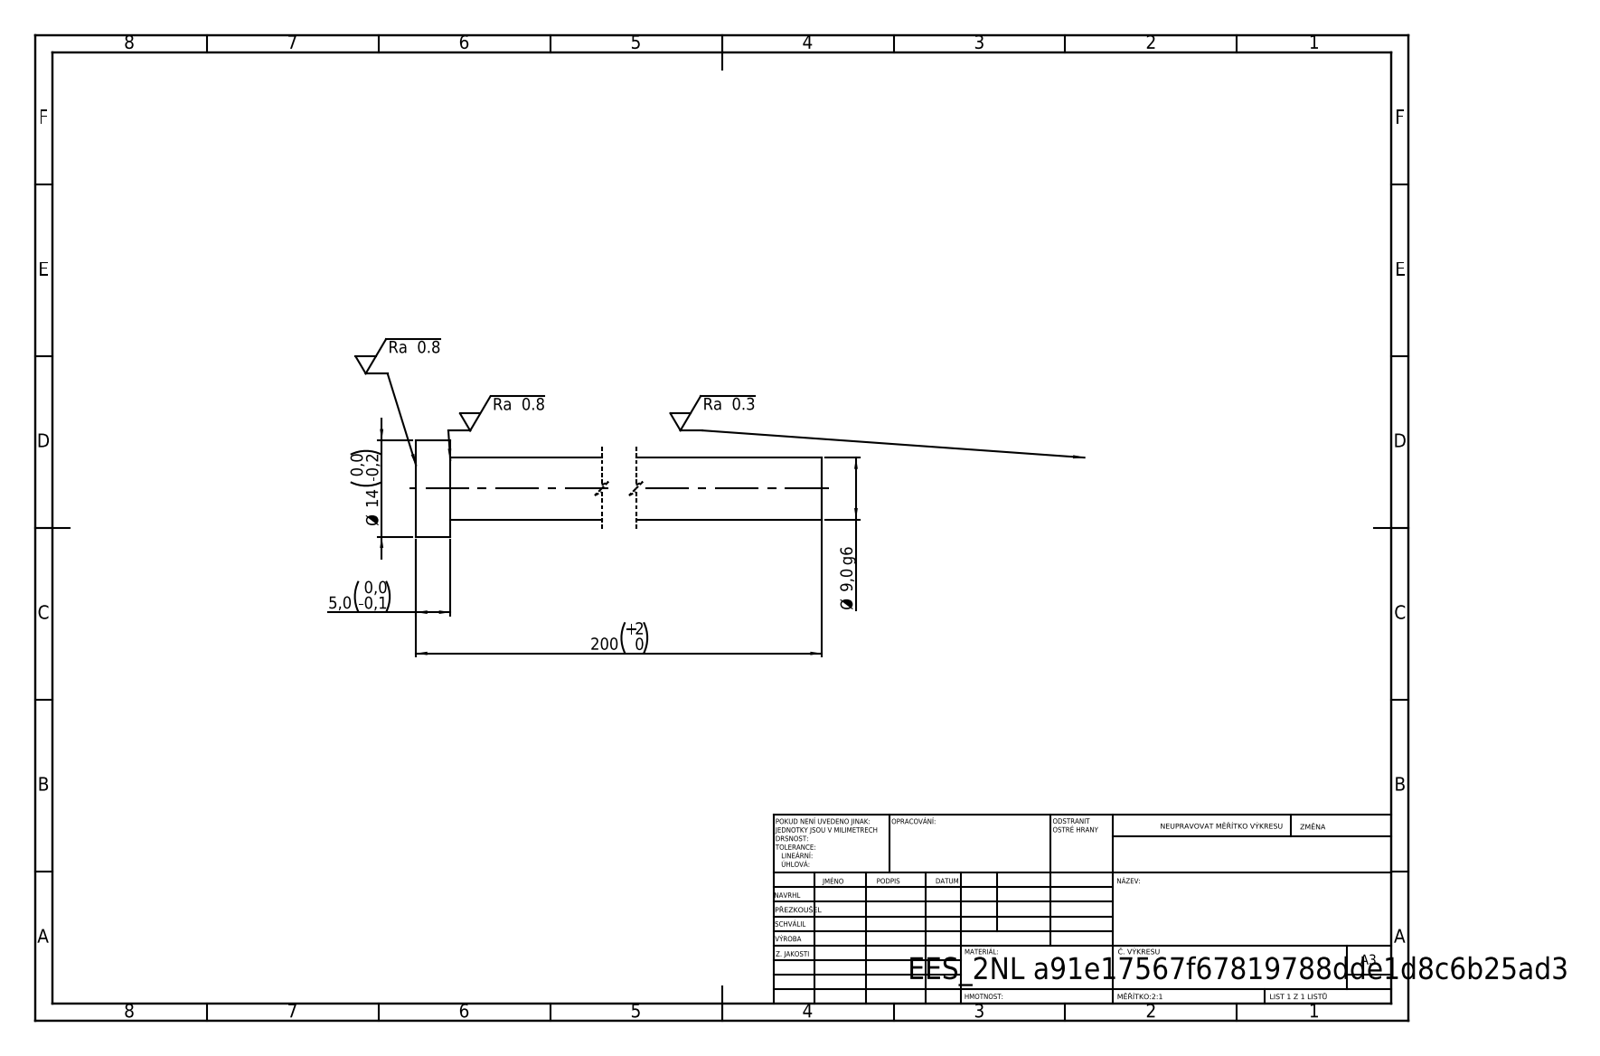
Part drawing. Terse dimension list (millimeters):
written by: SolidWorks 2019 (CONFIG_CONTROL_DESIGN)
unit: mm
bodies: 1 solid, 7 faces (3 planar, 4 cylindrical, 0 other)
size: 200 × 14 × 14
volume: 13 175 mm³; area: 6 041 mm²
bosses: 1× ⌀14, 1× ⌀9
face distances: 5, 200, 195
